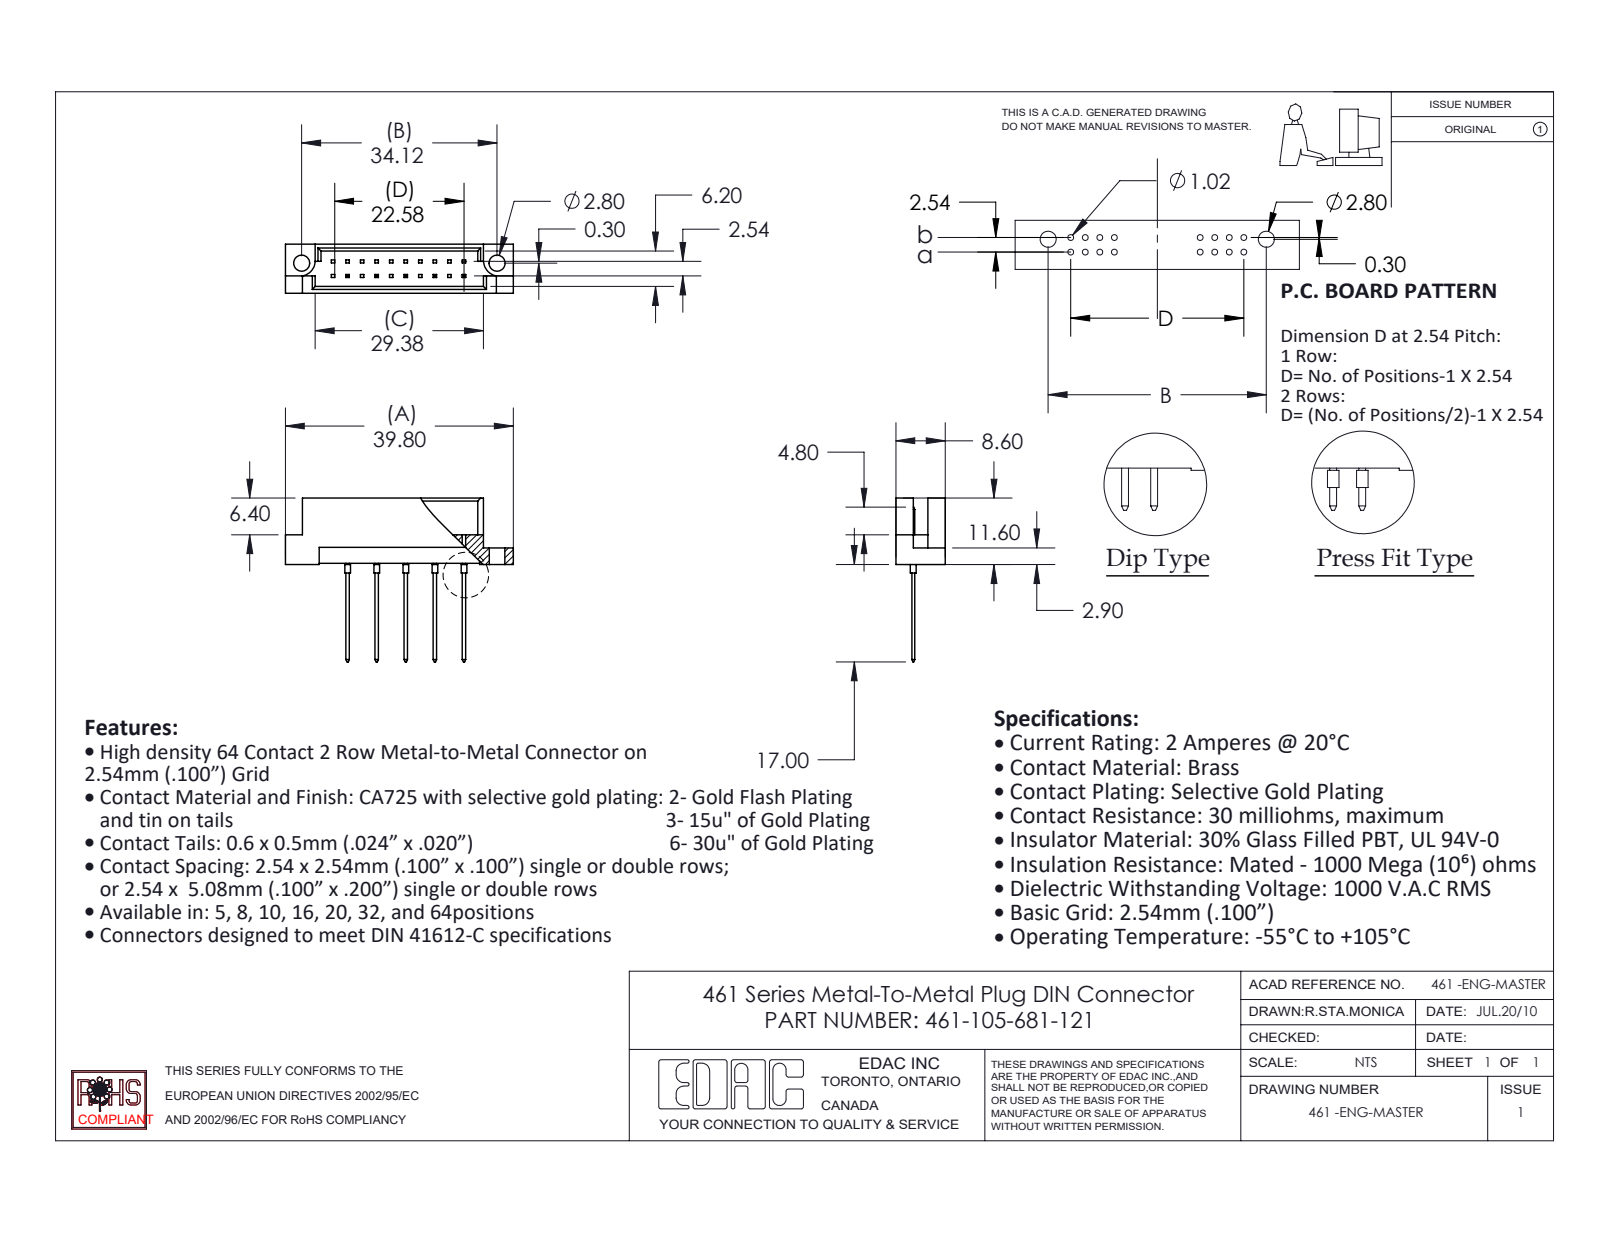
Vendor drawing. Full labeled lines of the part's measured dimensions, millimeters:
Part name (STEP PRODUCT): 461-290_81; 461-105-681-121; 461 Part_20
STEP written by: SolidWorks 2020 (CONFIG_CONTROL_DESIGN)
Units: millimetres
Bodies: 6 solids, 238 faces (222 planar, 16 cylindrical, 0 other)
Overall size (bounding box): 39.8 × 28.6 × 8.6
Volume: 1 948 mm³ · Surface area: 2 645 mm²
Round holes (diameter × count): ⌀2.8 ×2
Round bosses / shafts (diameter × count): ⌀1 ×5
Partial cylindrical surfaces — rounded edges, fillets, slot ends (radius × count): R2.8 ×2
Main face-to-face distances: 1.2, 7.4, 8.6, 6.2, 5, 5.08, 3.28, 5.32, 2.08, 4.12
Hole centre spacings: 34.12
